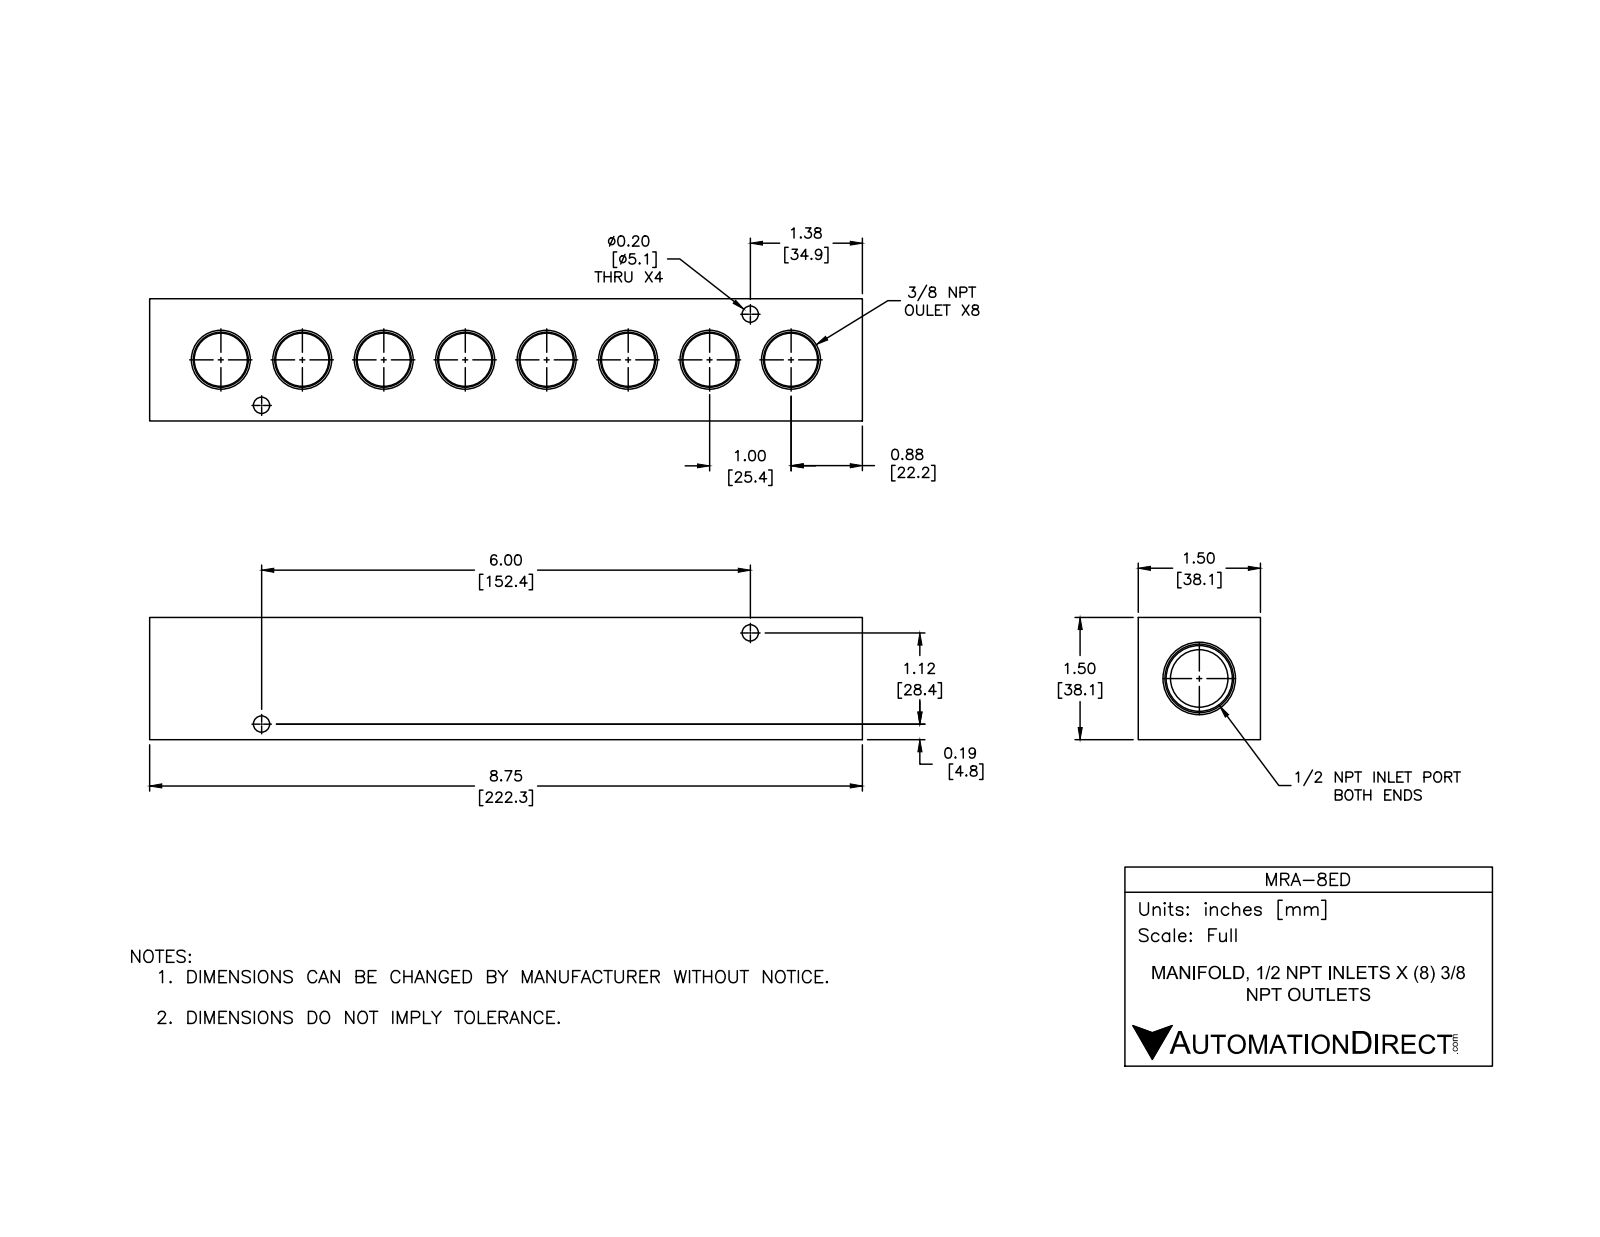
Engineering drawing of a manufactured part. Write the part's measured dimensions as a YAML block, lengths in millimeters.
part_name: "MRA-8ED"
step_written_by: "SolidWorks 2015 (CONFIG_CONTROL_DESIGN)"
units: millimeters
bodies: {solids: 1, faces: 98, planar: 24, cylindrical: 34, other: 40}
overall_size: [222.3, 38.1, 38.1]
volume: 242200
surface_area: 52730
round_holes:
  - {diameter: 14.3, count: 8}
  - {diameter: 5.1, count: 4}
  - {diameter: 17.9, count: 1}
face_to_face_distances: [38.1, 222.3, 27.7, 10.4, 13.5, 208.8, 195.3]
hole_center_spacings: [25.4, 50.8, 76.2, 19.1, 101.6, 127, 40.7, 65.1]
